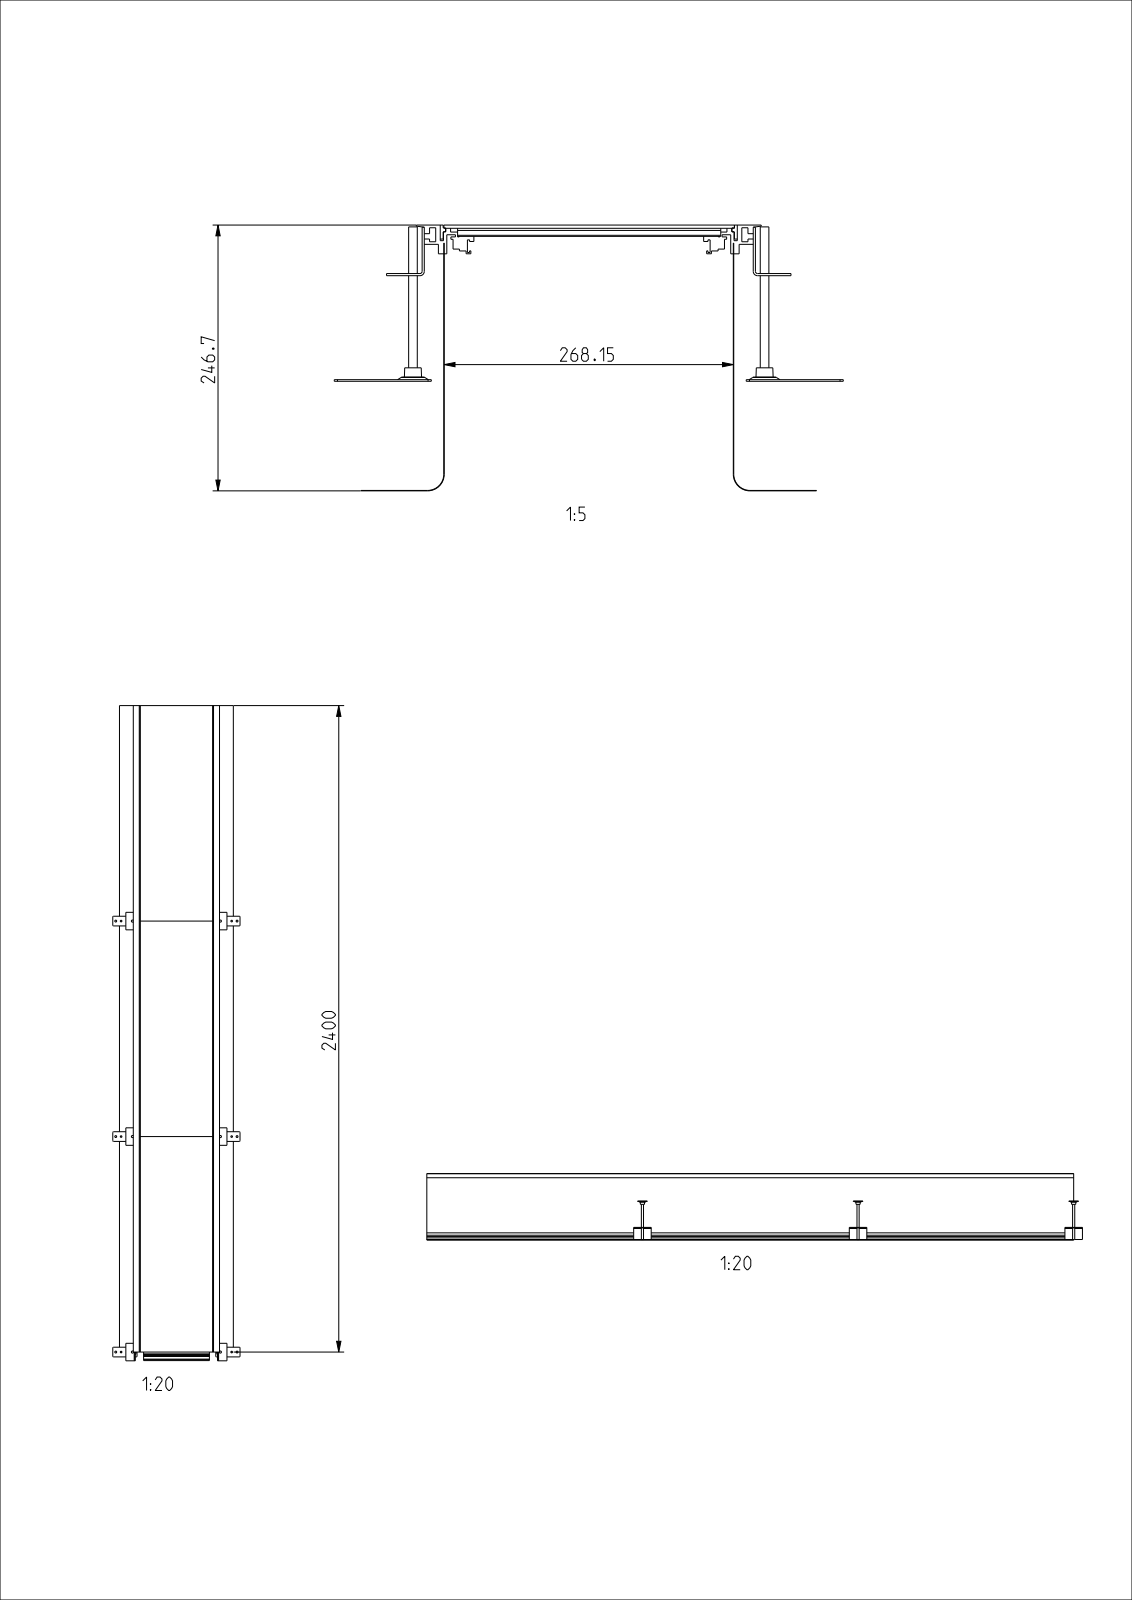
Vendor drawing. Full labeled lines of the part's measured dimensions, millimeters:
Part name (STEP PRODUCT): U05644KUN; U05650KUN; U05985KUN; U05347KUN (+8 more)
STEP written by: CREO PARAMETRIC BY PTC INC, 2020281 (AUTOMOTIVE_DESIGN)
Units: millimetres
Bodies: 41 solids, 720 faces (474 planar, 210 cylindrical, 36 other)
Overall size (bounding box): 2432.5 × 472.13 × 246.7
Volume: 6 003 000 mm³ · Surface area: 6 158 000 mm²
Round holes (diameter × count): ⌀6 ×6, ⌀7 ×6, ⌀8.5 ×6, ⌀11.5 ×6, ⌀17.5 ×6, ⌀23 ×6
Round bosses / shafts (diameter × count): ⌀20 ×6, ⌀8 ×6
Partial cylindrical surfaces — rounded edges, fillets, slot ends (radius × count): R2 ×62, R3 ×24, R0.5 ×14, R4 ×2, R15 ×2, R15.4 ×2
Main face-to-face distances: 0.4, 268.55, 3, 268.95, 268.15, 243.7, 246.7, 243.3, 246.3, 6.5
Hole centre spacings: 800, 800.25, 801.1, 802.4, 880.64, 889.18, 908.3, 20
